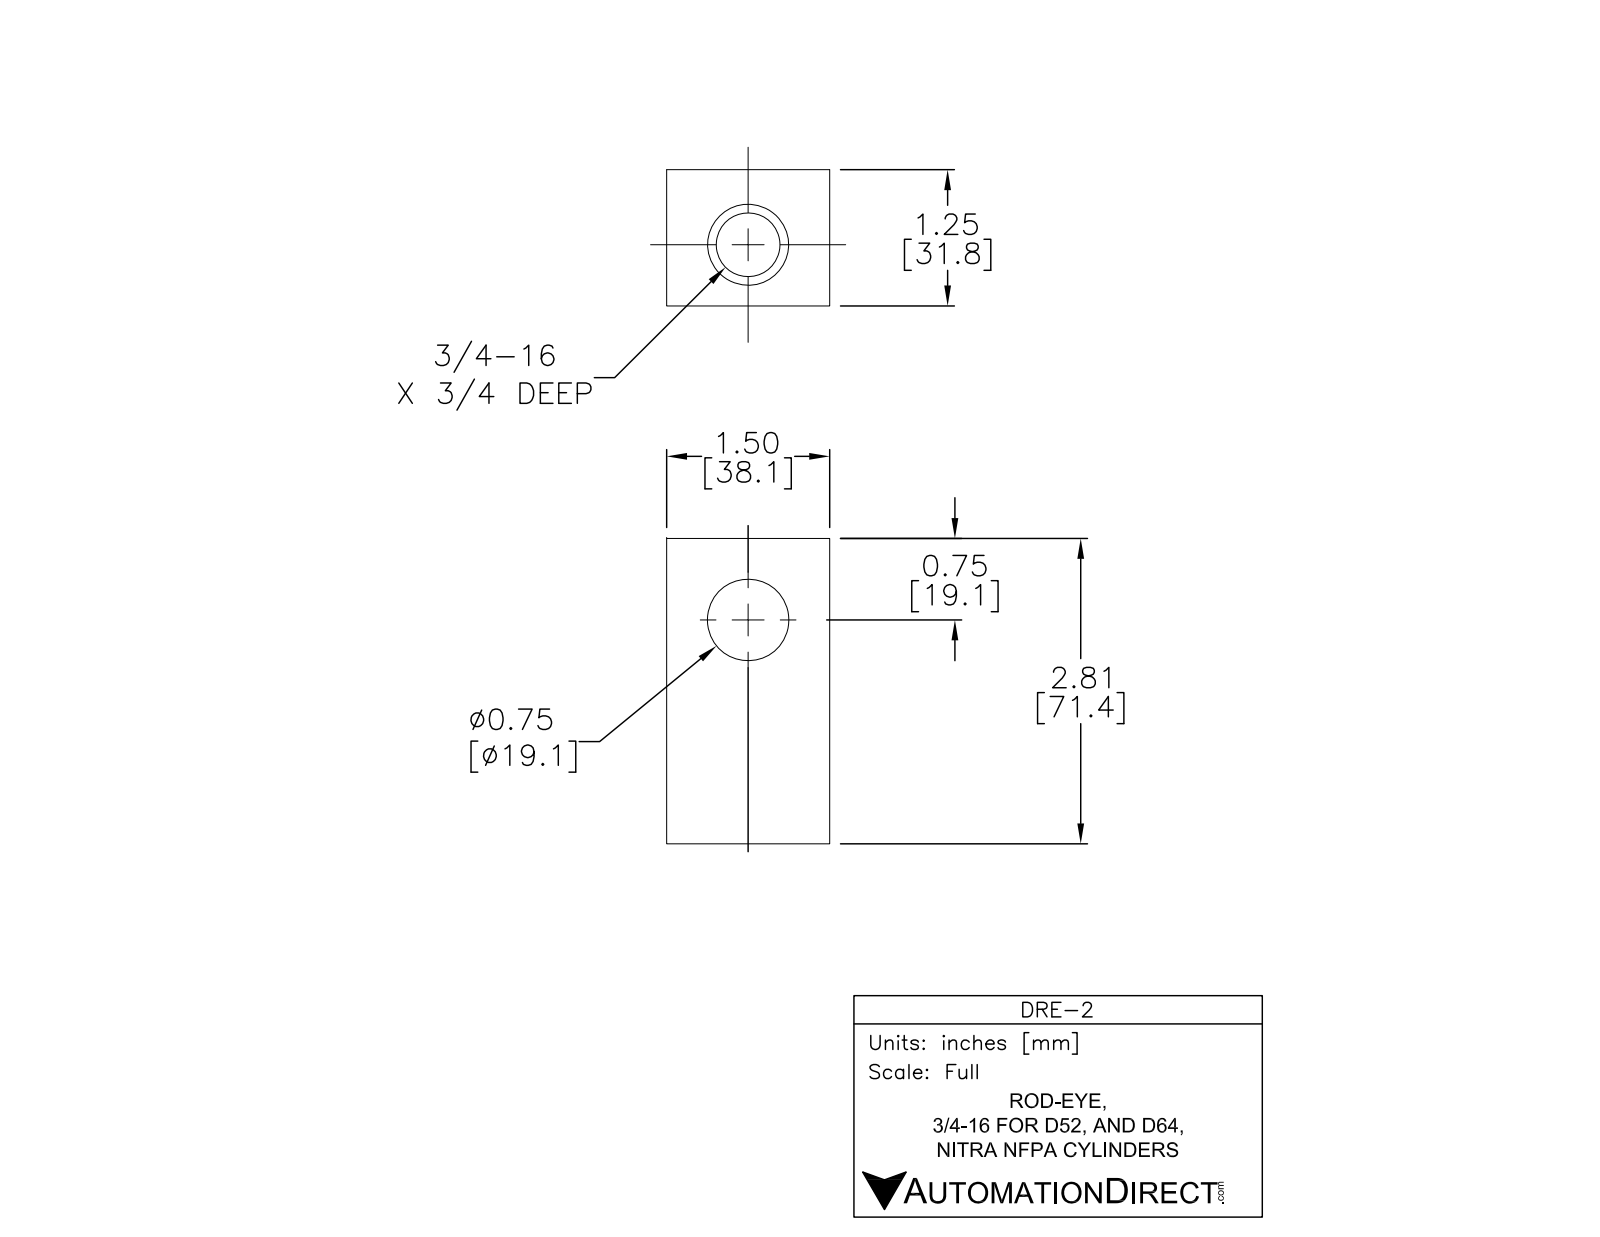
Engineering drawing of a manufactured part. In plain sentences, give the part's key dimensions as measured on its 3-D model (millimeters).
The part is named "DRE-2". Its 3-D file was written by "SolidWorks 2015 (AUTOMOTIVE_DESIGN)". It is 1 solid with 12 faces: 6 planar, 4 cylindrical and 2 other. Overall it measures 71.5 by 38.1 by 31.8 millimeters. Its volume is 68 960 cubic millimeters and its surface area 15 600 square millimeters. Round holes: 1 of diameter 17.4, 1 of diameter 19.1. The main face-to-face distances are 31.8, 38.1, 71.5.
